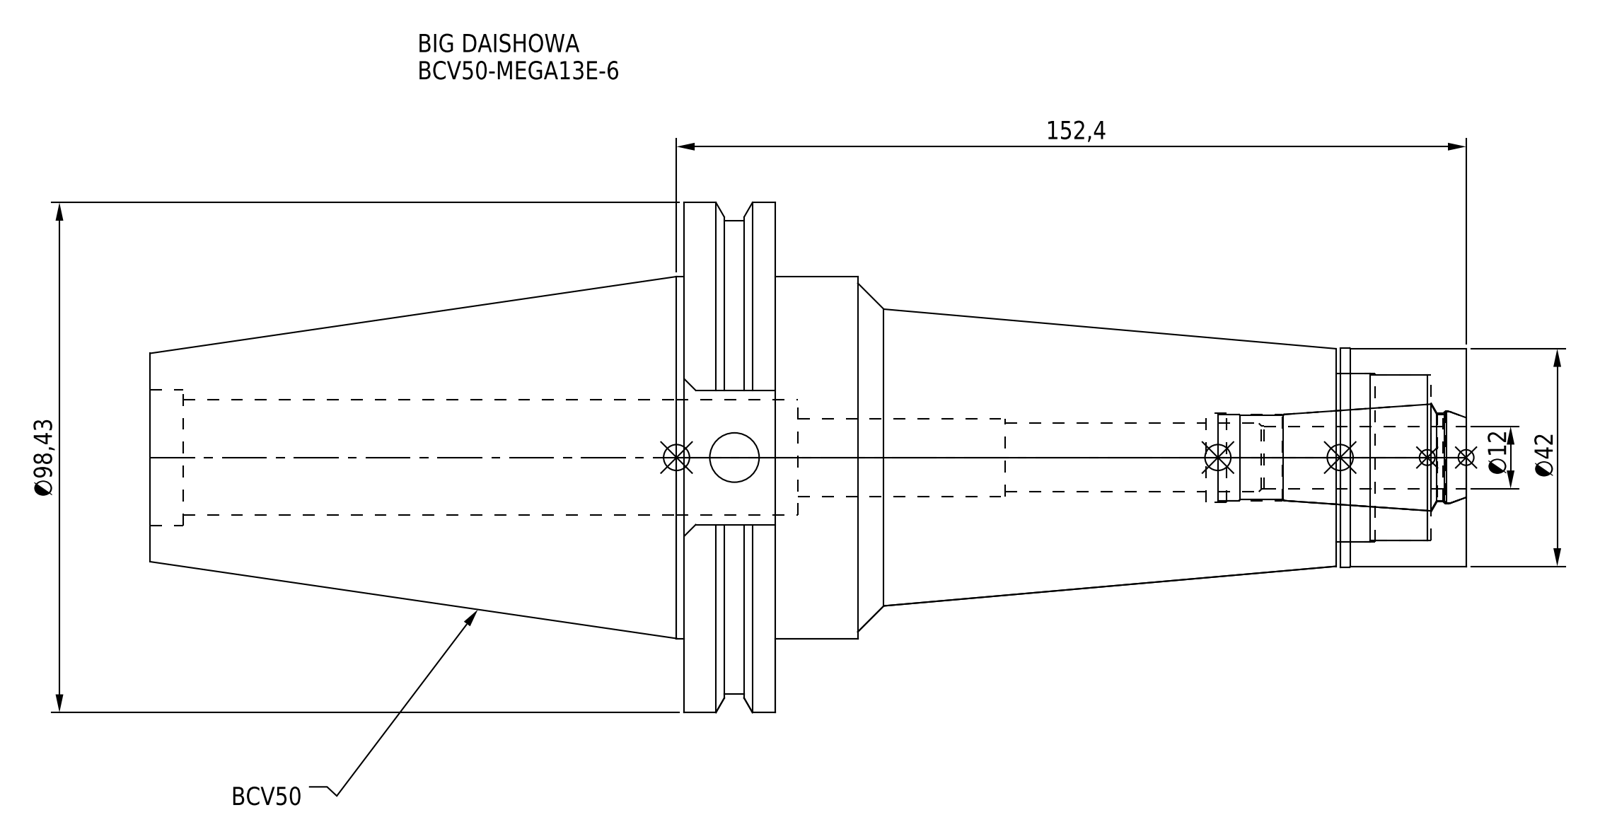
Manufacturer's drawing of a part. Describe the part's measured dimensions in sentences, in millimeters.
The part is named "BCV50-MEGA13E-6-120.stp; MEN13_1.stp; BCV50-MEGA13E-6_1.stp; DXF_TEMP_ASSY_ASM_4_ASM.stp (+3 more)". Its 3-D file was written by "SolidWorks 2019 (CONFIG_CONTROL_DESIGN)". It is 2 solids with 93 faces: 31 planar, 42 cylindrical and 20 other. Overall it measures 254 by 98.42 by 94.95 millimeters. Its volume is 576 880 cubic millimeters and its surface area 76 849 square millimeters. Round holes: 1 of diameter 9.53, 1 of diameter 13.3, 1 of diameter 15, 1 of diameter 16.6, 1 of diameter 17, 1 of diameter 17.2, 1 of diameter 17.9, 1 of diameter 22.3, 1 of diameter 26.23, 1 of diameter 32, 1 of diameter 32.5. Round bosses or shafts: 1 of diameter 98.42, 1 of diameter 91.29, 1 of diameter 69.85, 1 of diameter 42.3, 1 of diameter 42. The main face-to-face distances are 17.55, 133.35, 150.9, 254, 120.65, 103.1, 25.1, 24.3, 109.05, 126.6.
